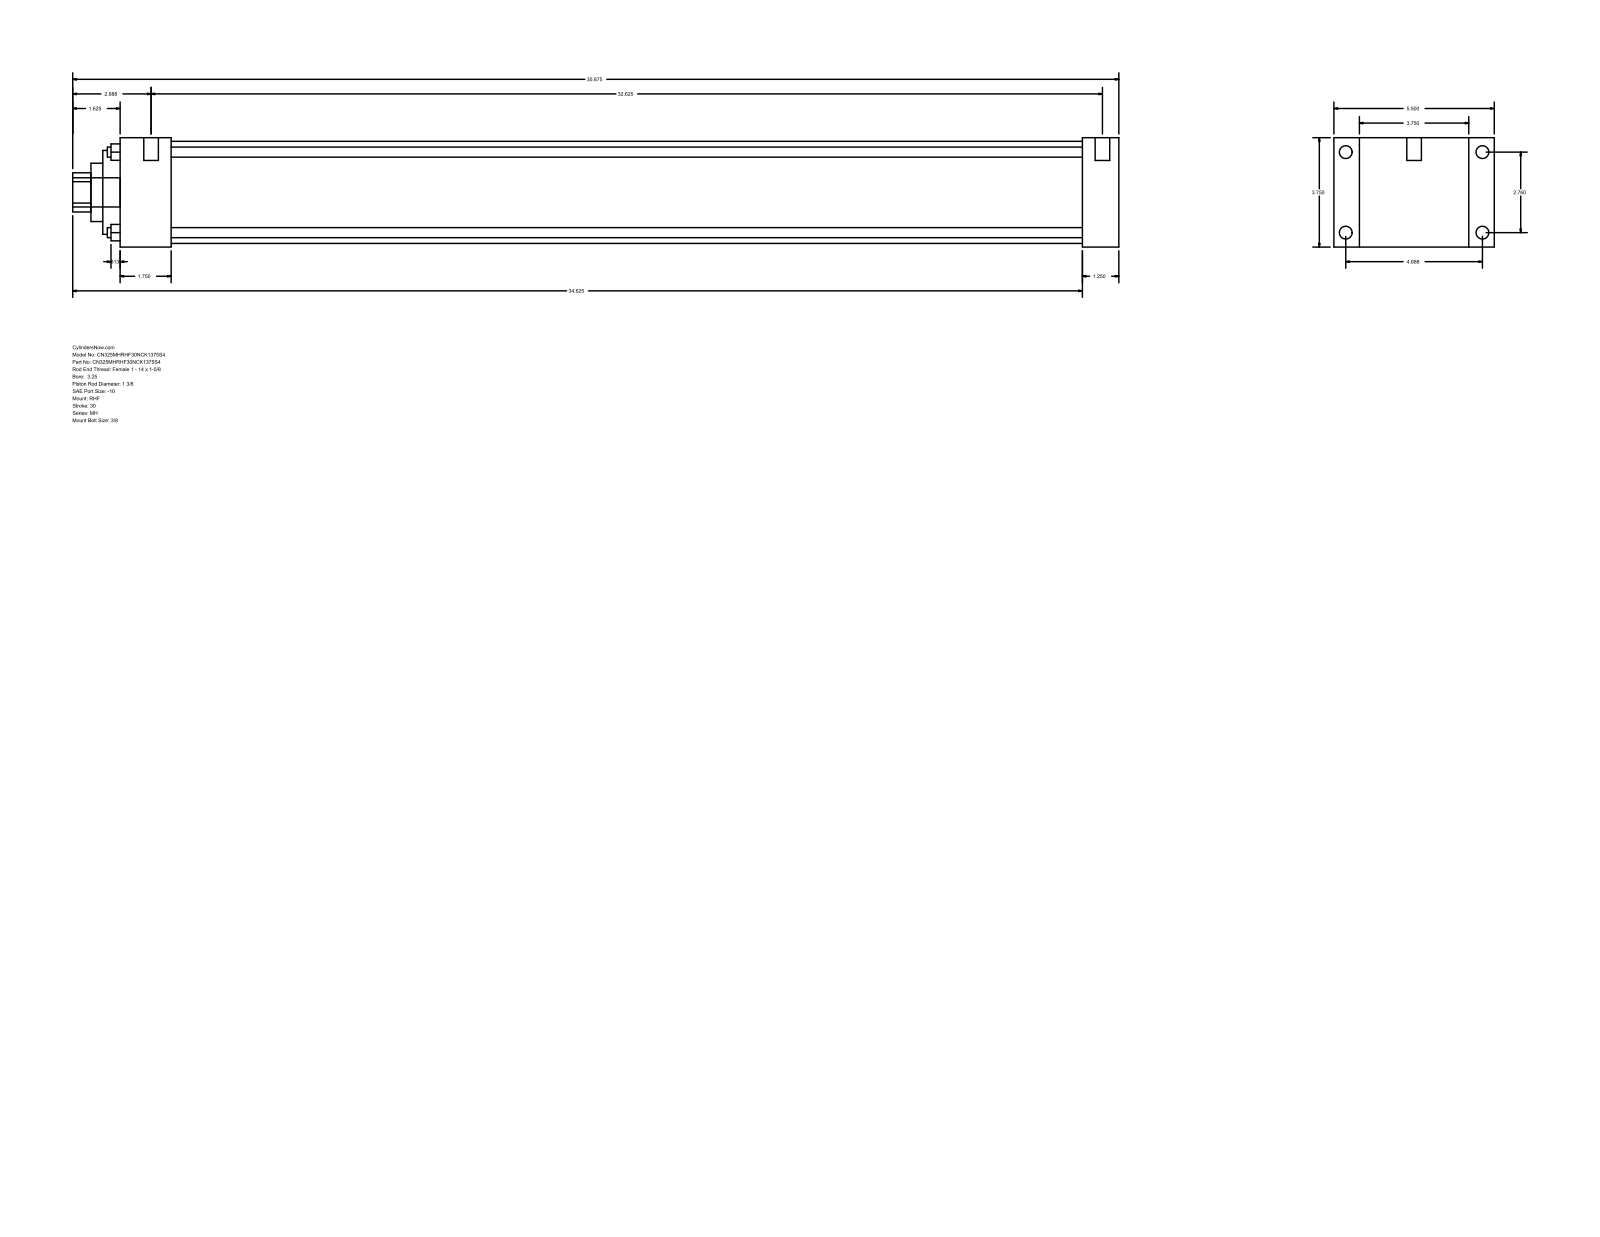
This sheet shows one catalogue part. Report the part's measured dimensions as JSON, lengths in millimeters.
{"part_name": "MH_RHF__0325_1.375", "step_written_by": "GSSL Pune (CONFIG_CONTROL_DESIGN)", "units": "millimeters", "bodies": {"solids": 0, "faces": 90, "planar": 61, "cylindrical": 29, "other": 0}, "overall_size": [911.23, 139.7, 95.25], "round_holes": [[8.76, 4], [34.92, 1], [50.8, 1], [73.03, 1], [88.9, 1]], "round_bosses_or_shafts": [[11.13, 4], [5.56, 4], [12.7, 2], [25.4, 1]], "partial_cylinders_radius": [[17.06, 1]], "face_to_face_distances": [95.24, 31.75, 22.23, 117.47, 838.21, 869.96, 139.7, 44.45, 793.76, 825.51], "hole_center_spacings": [49.57, 70.1, 99.14]}
